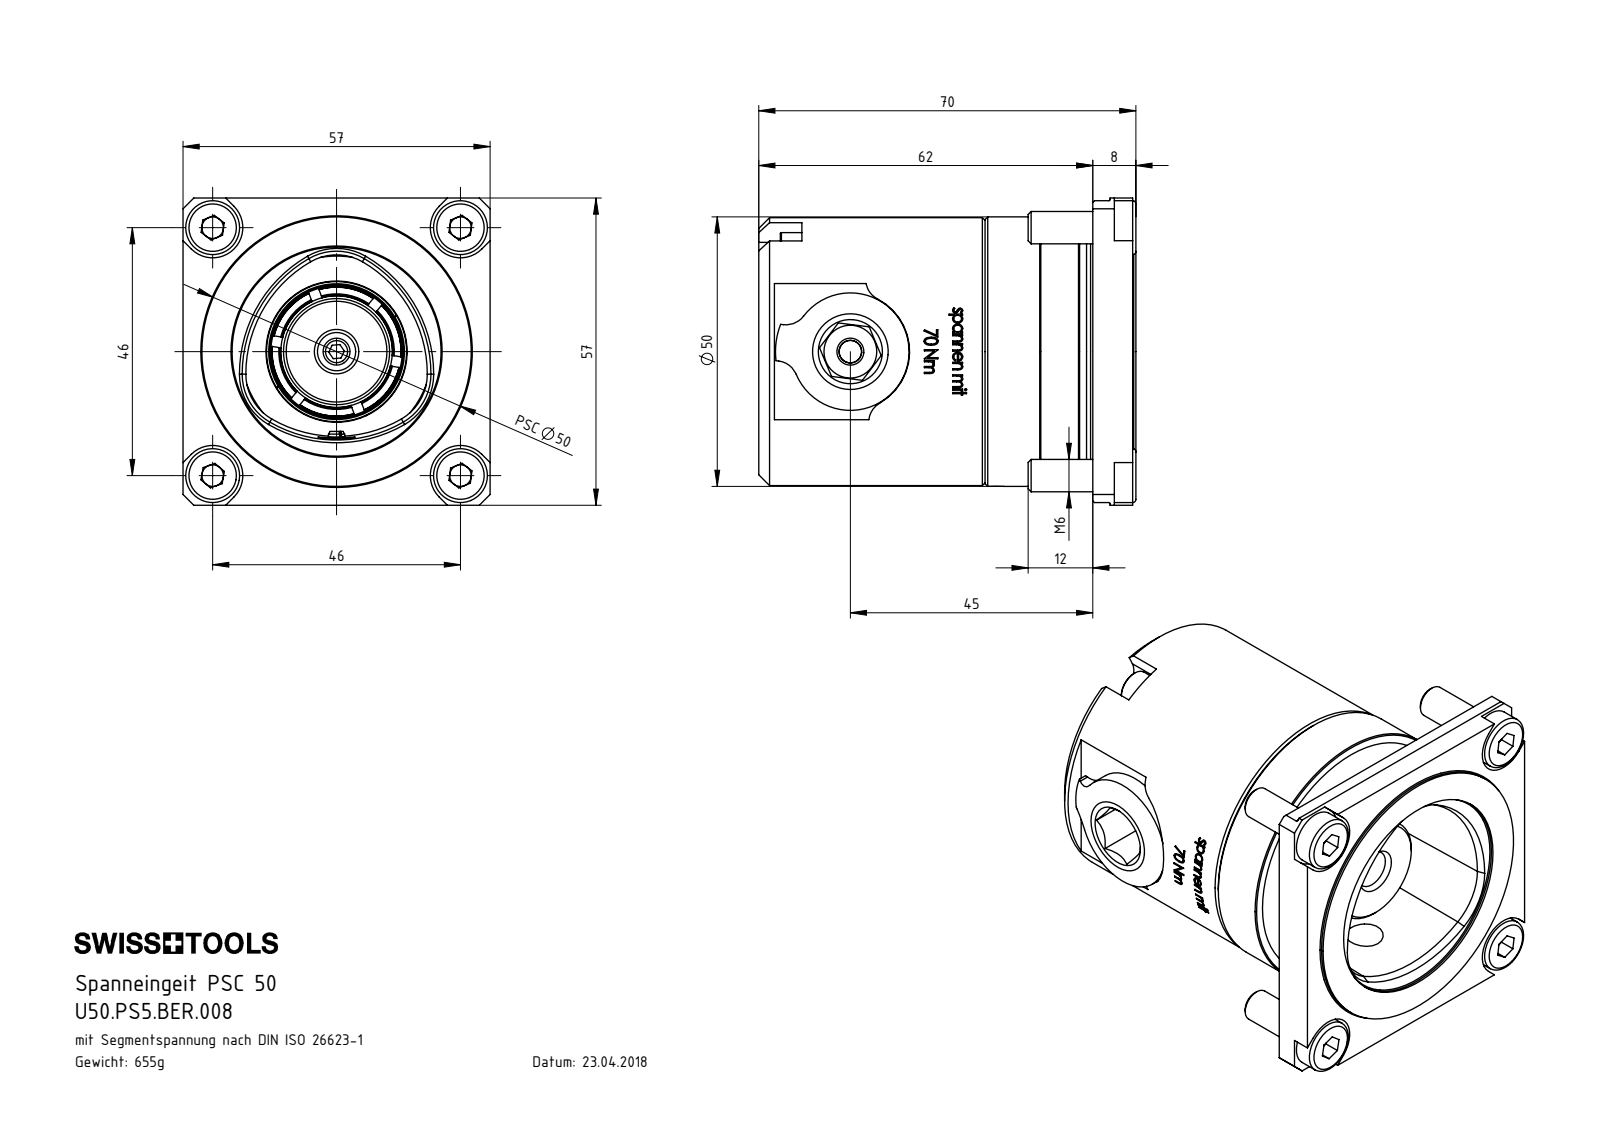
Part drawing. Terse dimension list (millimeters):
name: 986.19200.000.1; ISO 4026 - M5 x 5; O-Ring_1.50-AD31.50; U50-PS5.BER.042_B (+8 more)
written by: SolidWorks 2017 (AUTOMOTIVE_DESIGN)
unit: mm
bodies: 27 solids, 754 faces (292 planar, 180 cylindrical, 282 other)
size: 70 × 57.5 × 57
volume: 111 136 mm³; area: 52 867 mm²
holes: 4× ⌀4.2, 4× ⌀6.2, 3× ⌀2.1, 3× ⌀3, 2× ⌀3.3, 2× ⌀4.17, 1× ⌀7, 1× ⌀7.1, 1× ⌀9.8, 1× ⌀12, 1× ⌀12.8, 1× ⌀12.97
bosses: 4× ⌀10, 4× ⌀6, 2× ⌀7, 2× ⌀4, 1× ⌀50, 1× ⌀49.7, 1× ⌀46.5, 1× ⌀42
rounds: 12× R0.3, 4× R5, 4× R5.6, 2× R0.2, 2× R4, 2× R4.05, 2× R4.1, 1× R11
face distances: 4, 28, 24, 8, 38, 31.4, 62, 20, 32, 0.6
hole spacings: 32.53, 46, 12.5, 15.01, 20.5, 31.97, 43.98, 52.26
